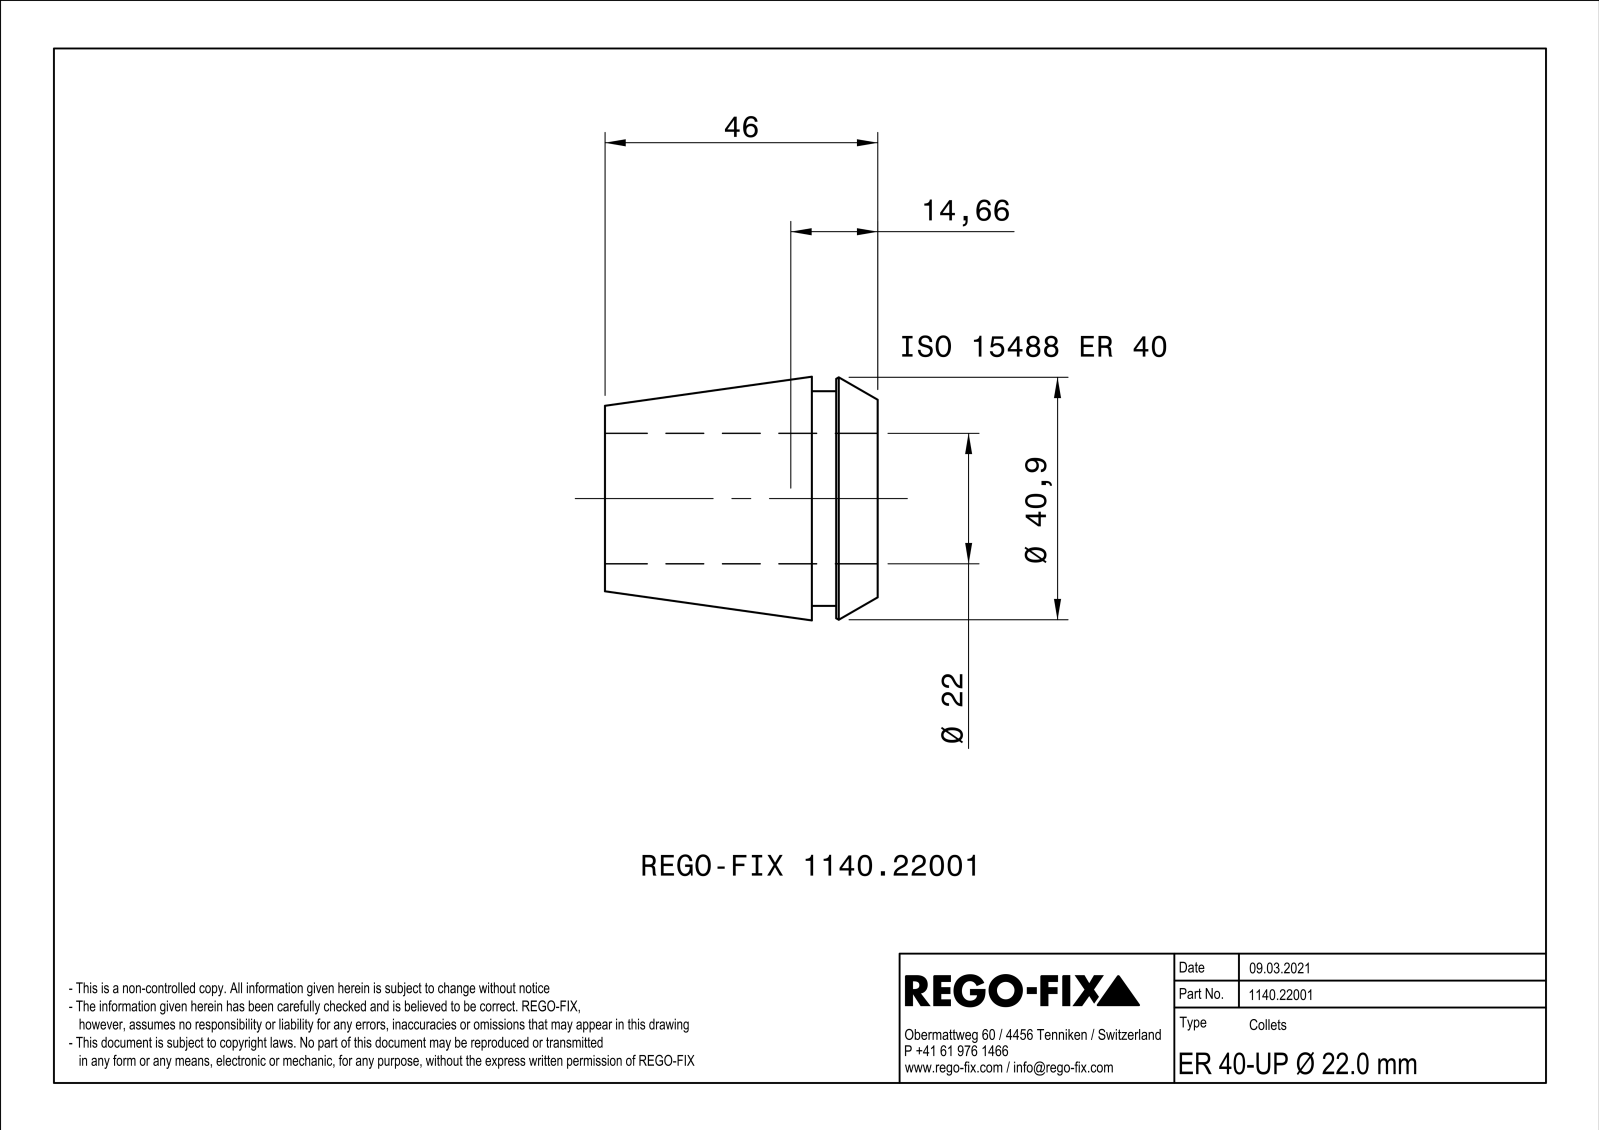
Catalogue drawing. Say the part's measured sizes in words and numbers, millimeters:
The part is named "NOCUT". Its 3-D file was written by "SIEMENS PLM Software Solid Edge ST10 (AUTOMOTIVE_DESIGN)". It is 1 solid with 177 faces: 88 planar, 9 cylindrical and 80 other. Overall it measures 46 by 40.99 by 40.99 millimeters. Its volume is 25 680 cubic millimeters and its surface area 17 941 square millimeters. Round holes: 1 of diameter 22. Round bosses or shafts: 1 of diameter 36.2. The main face-to-face distances are 1, 46, 11.1, 34.9, 7, 4.1, 39, 7.5, 0.5, 3.6.
